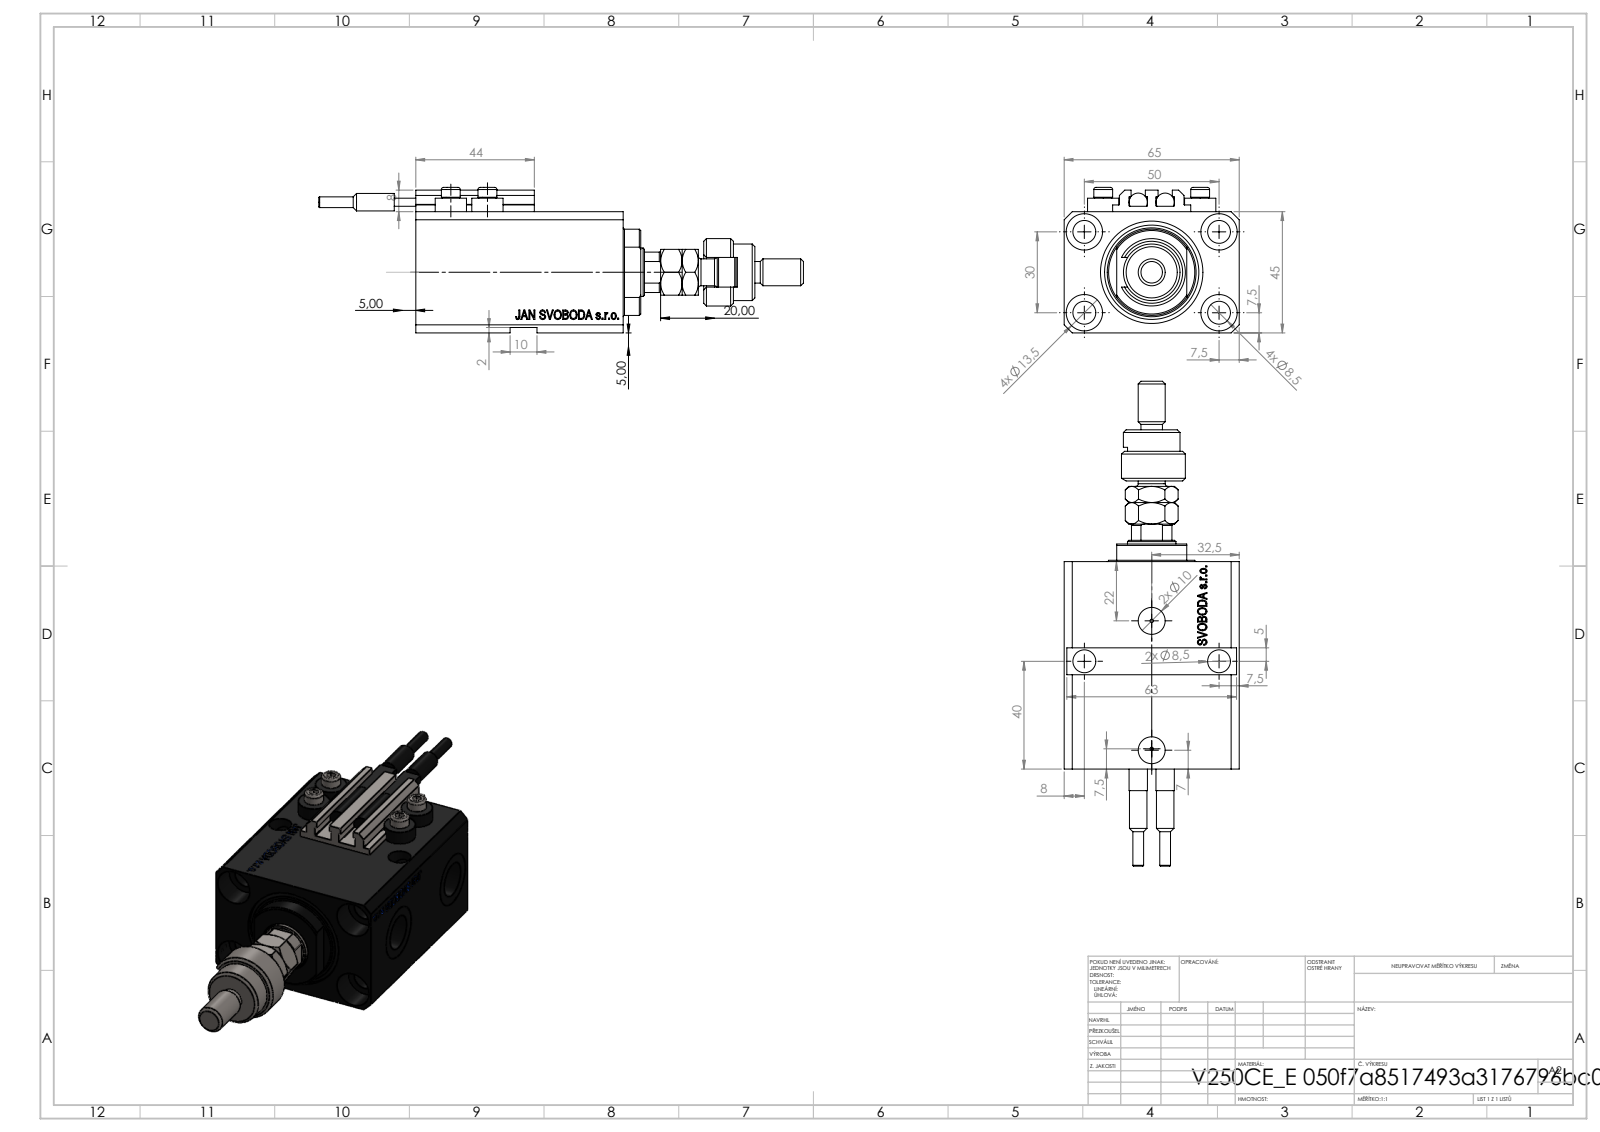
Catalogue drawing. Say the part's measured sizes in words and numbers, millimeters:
The part is named "V250CE_VC_E; FEMALE_PART_FOR_DFA; MFA; SWITCH_V250CE (+3 more)". Its 3-D file was written by "SolidWorks 2019 (CONFIG_CONTROL_DESIGN)". It is 12 solids with 1204 faces: 571 planar, 151 cylindrical and 482 other. Overall it measures 180 by 65 by 54 millimeters. Its volume is 215 142 cubic millimeters and its surface area 67 381 square millimeters. Round holes: 7 of diameter 8.5, 4 of diameter 1.25, 4 of diameter 4, 4 of diameter 13.5, 2 of diameter 10, 2 of diameter 13.16, 2 of diameter 20, 1 of diameter 18, 1 of diameter 38. Round bosses or shafts: 4 of diameter 11.6, 4 of diameter 7, 2 of diameter 6.8, 2 of diameter 6.5, 2 of diameter 4, 1 of diameter 25, 1 of diameter 21, 1 of diameter 16. Partial cylindrical surfaces (rounded edges, fillets, slot ends): 10 of radius 0.2, 1 of radius 5.5, 1 of radius 8.5, 1 of radius 8.75, 1 of radius 16. The main face-to-face distances are 45, 14, 65, 63, 2, 77, 3, 5, 47, 6.9. The hole center spacings are 29.15, 50, 13.6, 15.12, 18.81, 18.97, 26.22, 26.61.
